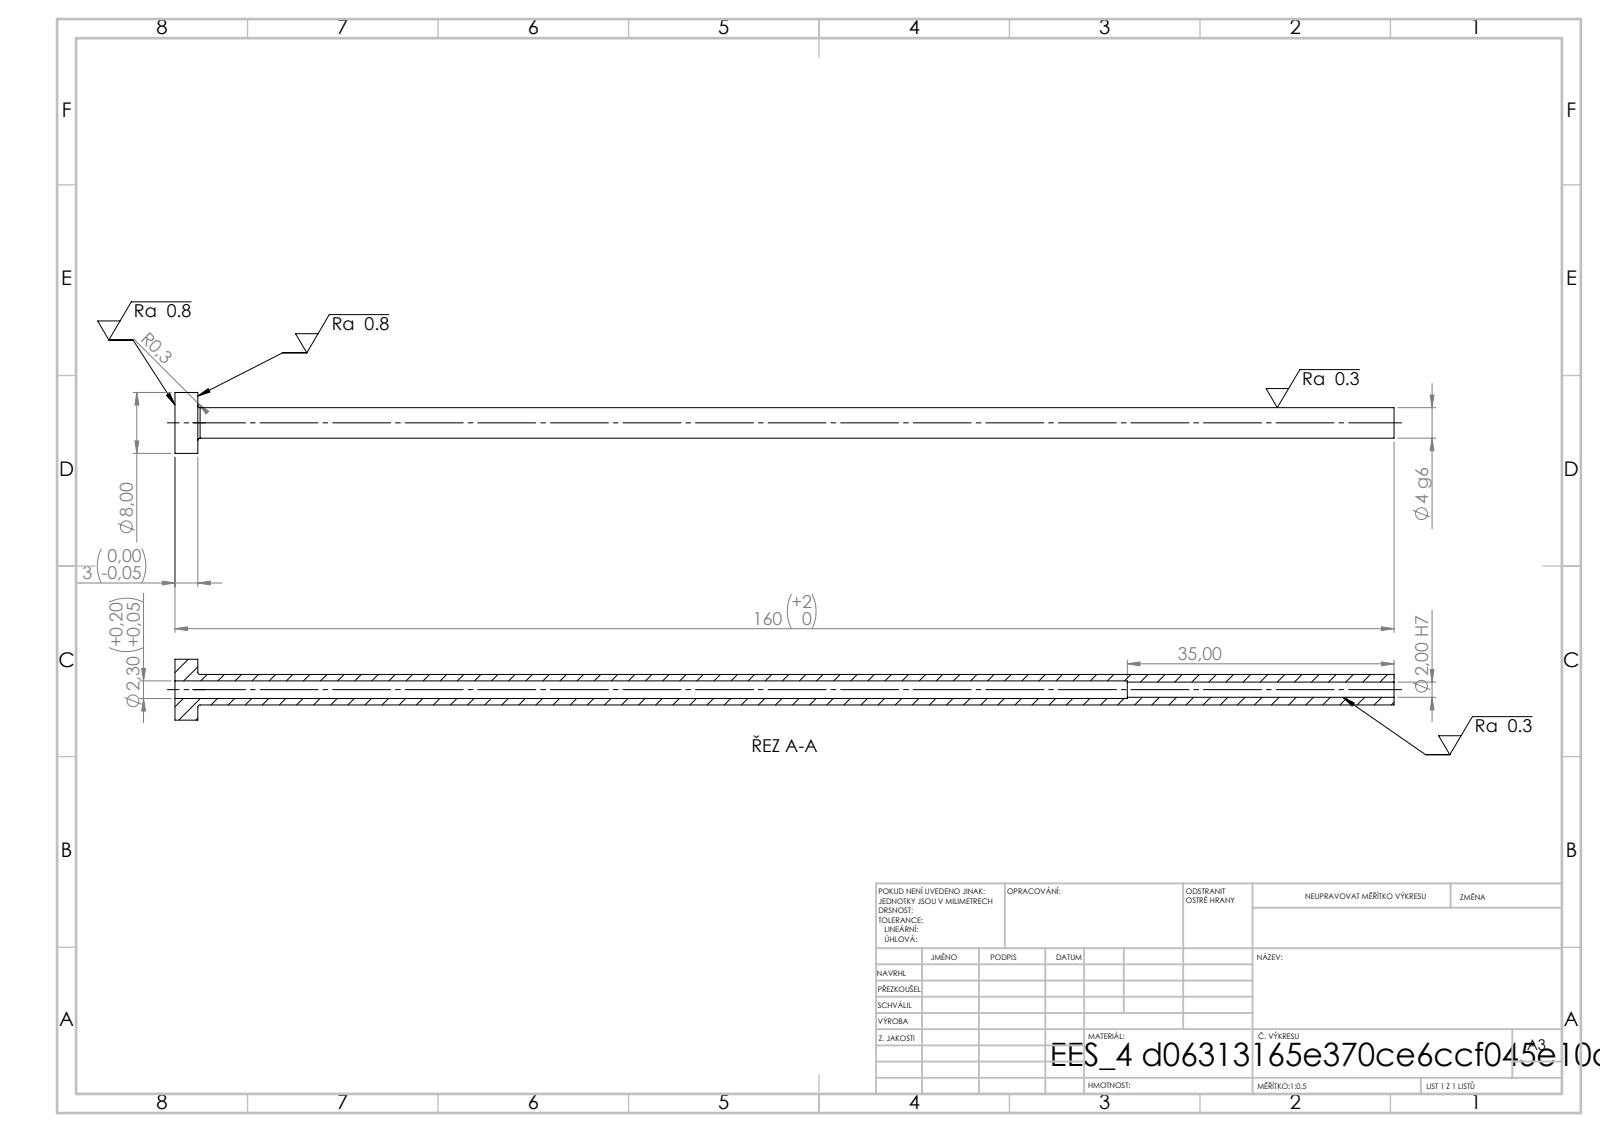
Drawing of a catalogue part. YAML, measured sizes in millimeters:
step_written_by: "SolidWorks 2019 (CONFIG_CONTROL_DESIGN)"
units: millimeters
bodies: {solids: 1, faces: 14, planar: 4, cylindrical: 8, other: 2}
overall_size: [160, 8, 8]
volume: 1495
surface_area: 3264
round_holes:
  - {diameter: 2, count: 1}
  - {diameter: 2.3, count: 1}
round_bosses_or_shafts:
  - {diameter: 8, count: 1}
  - {diameter: 4, count: 1}
face_to_face_distances: [3, 160, 157, 125, 122, 35]
